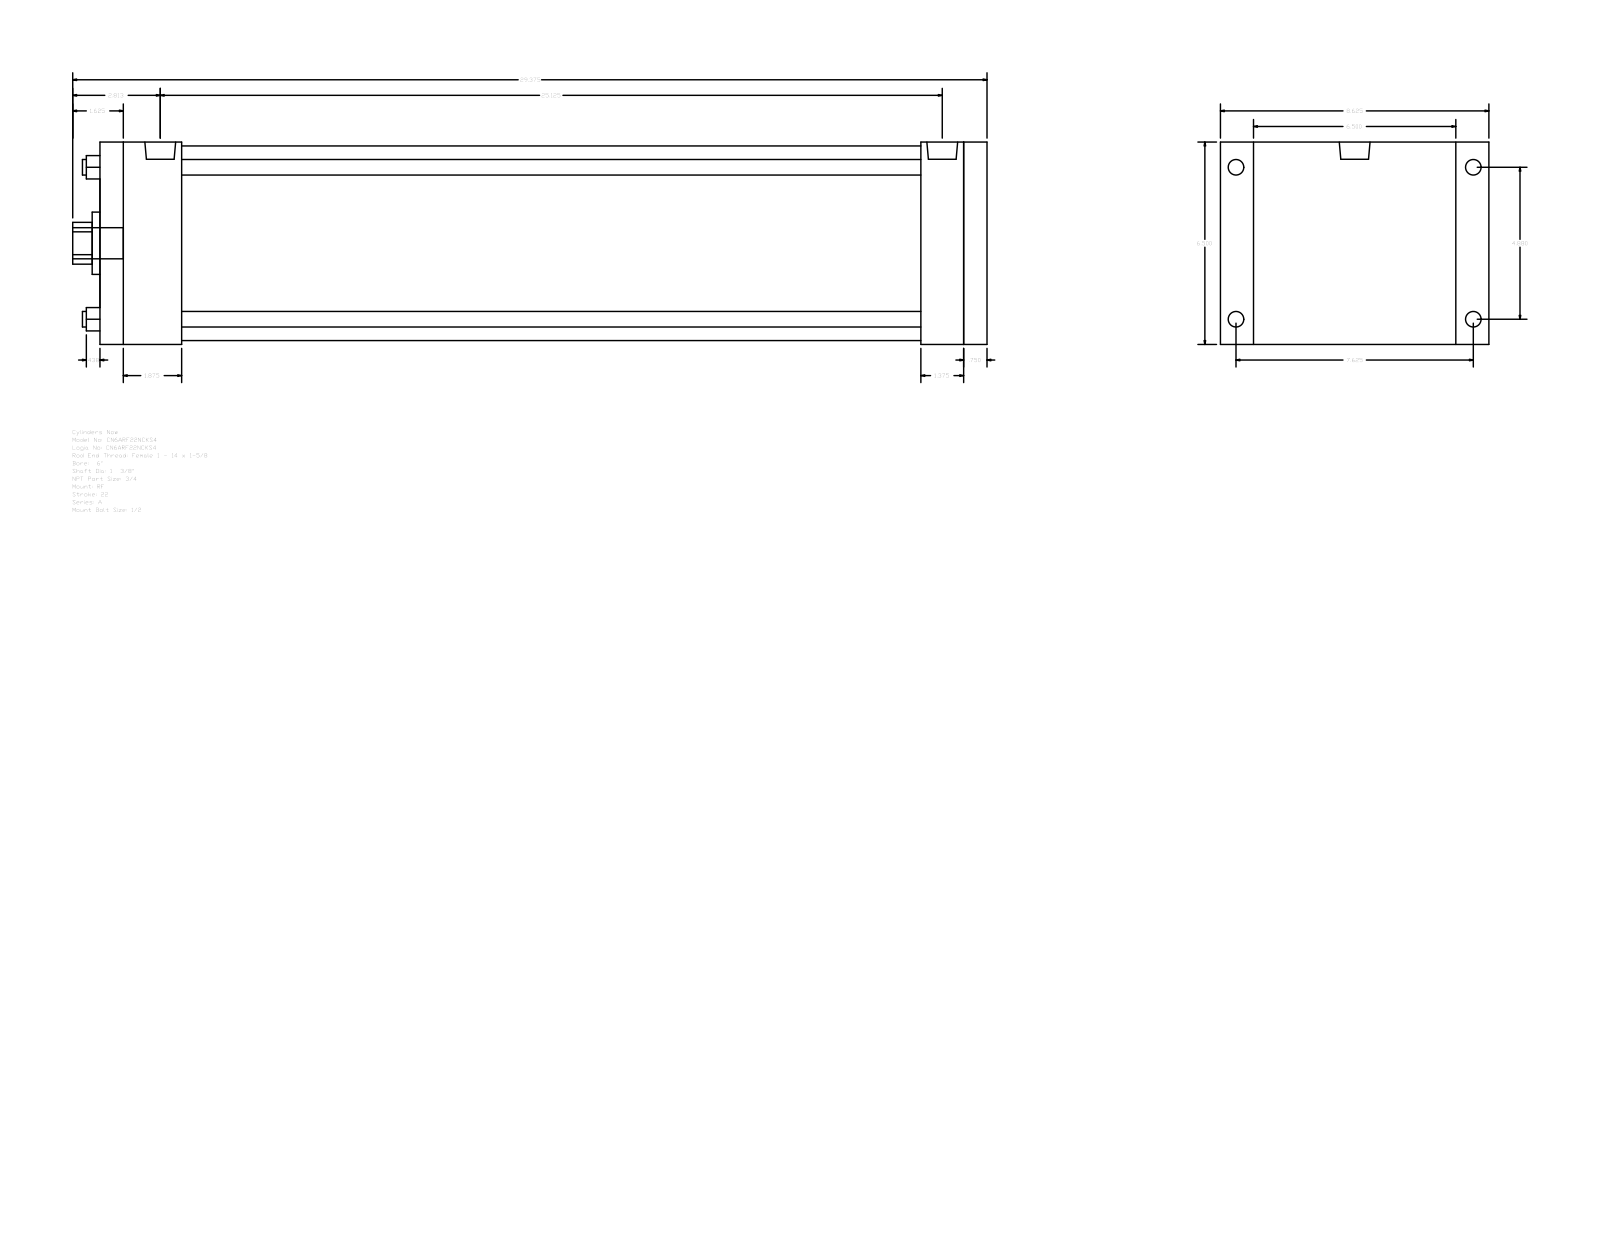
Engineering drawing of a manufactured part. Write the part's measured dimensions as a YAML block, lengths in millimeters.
part_name: "A_RF__0600_1.375"
step_written_by: "GSSL Pune (CONFIG_CONTROL_DESIGN)"
units: millimeters
bodies: {solids: 0, faces: 92, planar: 64, cylindrical: 28, other: 0}
overall_size: [746.12, 219.07, 165.1]
round_holes:
  - {diameter: 12.7, count: 4}
  - {diameter: 34.92, count: 1}
  - {diameter: 50.8, count: 1}
  - {diameter: 158.75, count: 1}
round_bosses_or_shafts:
  - {diameter: 15.08, count: 4}
  - {diameter: 12.7, count: 4}
  - {diameter: 25.12, count: 2}
  - {diameter: 25.4, count: 1}
partial_cylinders:
  - {radius: 17.06, count: 1}
face_to_face_distances: [165.1, 723.89, 19.04, 704.85, 66.67, 638.18, 657.22, 669.92, 603.25, 34.93]
hole_center_spacings: [87.65, 123.96, 175.31]
